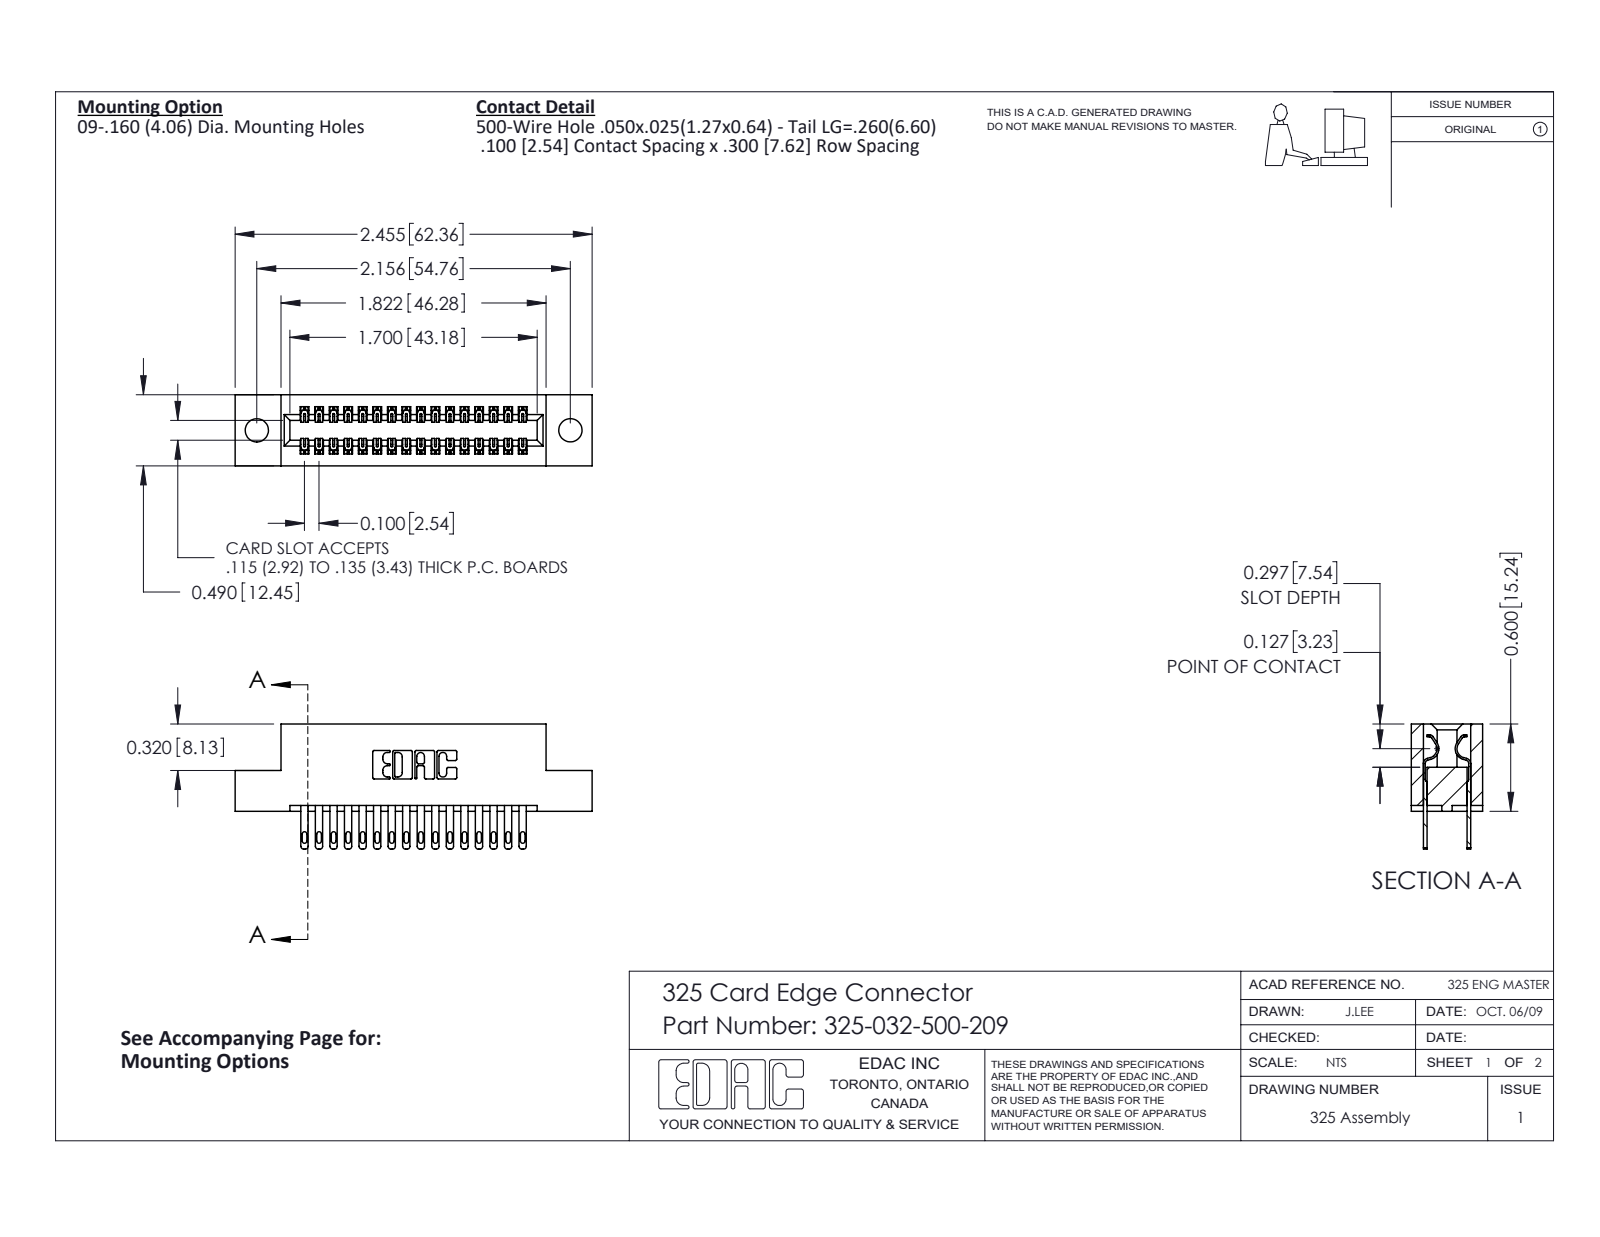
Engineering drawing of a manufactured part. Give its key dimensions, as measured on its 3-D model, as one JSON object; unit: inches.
{"part_name": "325 Part_.160 TH; 325-032-500-209; 325-292-001_325-293-100", "step_written_by": "SolidWorks 2016 (CONFIG_CONTROL_DESIGN)", "units": "inches", "bodies": {"solids": 33, "faces": 1650, "planar": 1030, "cylindrical": 620, "other": 0}, "overall_size": [2.455, 0.86, 0.49], "volume_in3": 0.469, "surface_area_in2": 13.85, "round_holes": [[0.16, 2]], "partial_cylinders_radius": [[0.006, 48], [0.016, 32], [0.02, 32], [0.01, 22], [0.007, 6], [0.031, 6], [0.026, 3], [0.014, 2]], "face_to_face_distances": [0.083, 0.407, 0.3, 0.107, 0.383, 0.025, 0.49, 0.325, 0.04, 0.1], "hole_center_spacings": [2.156]}
